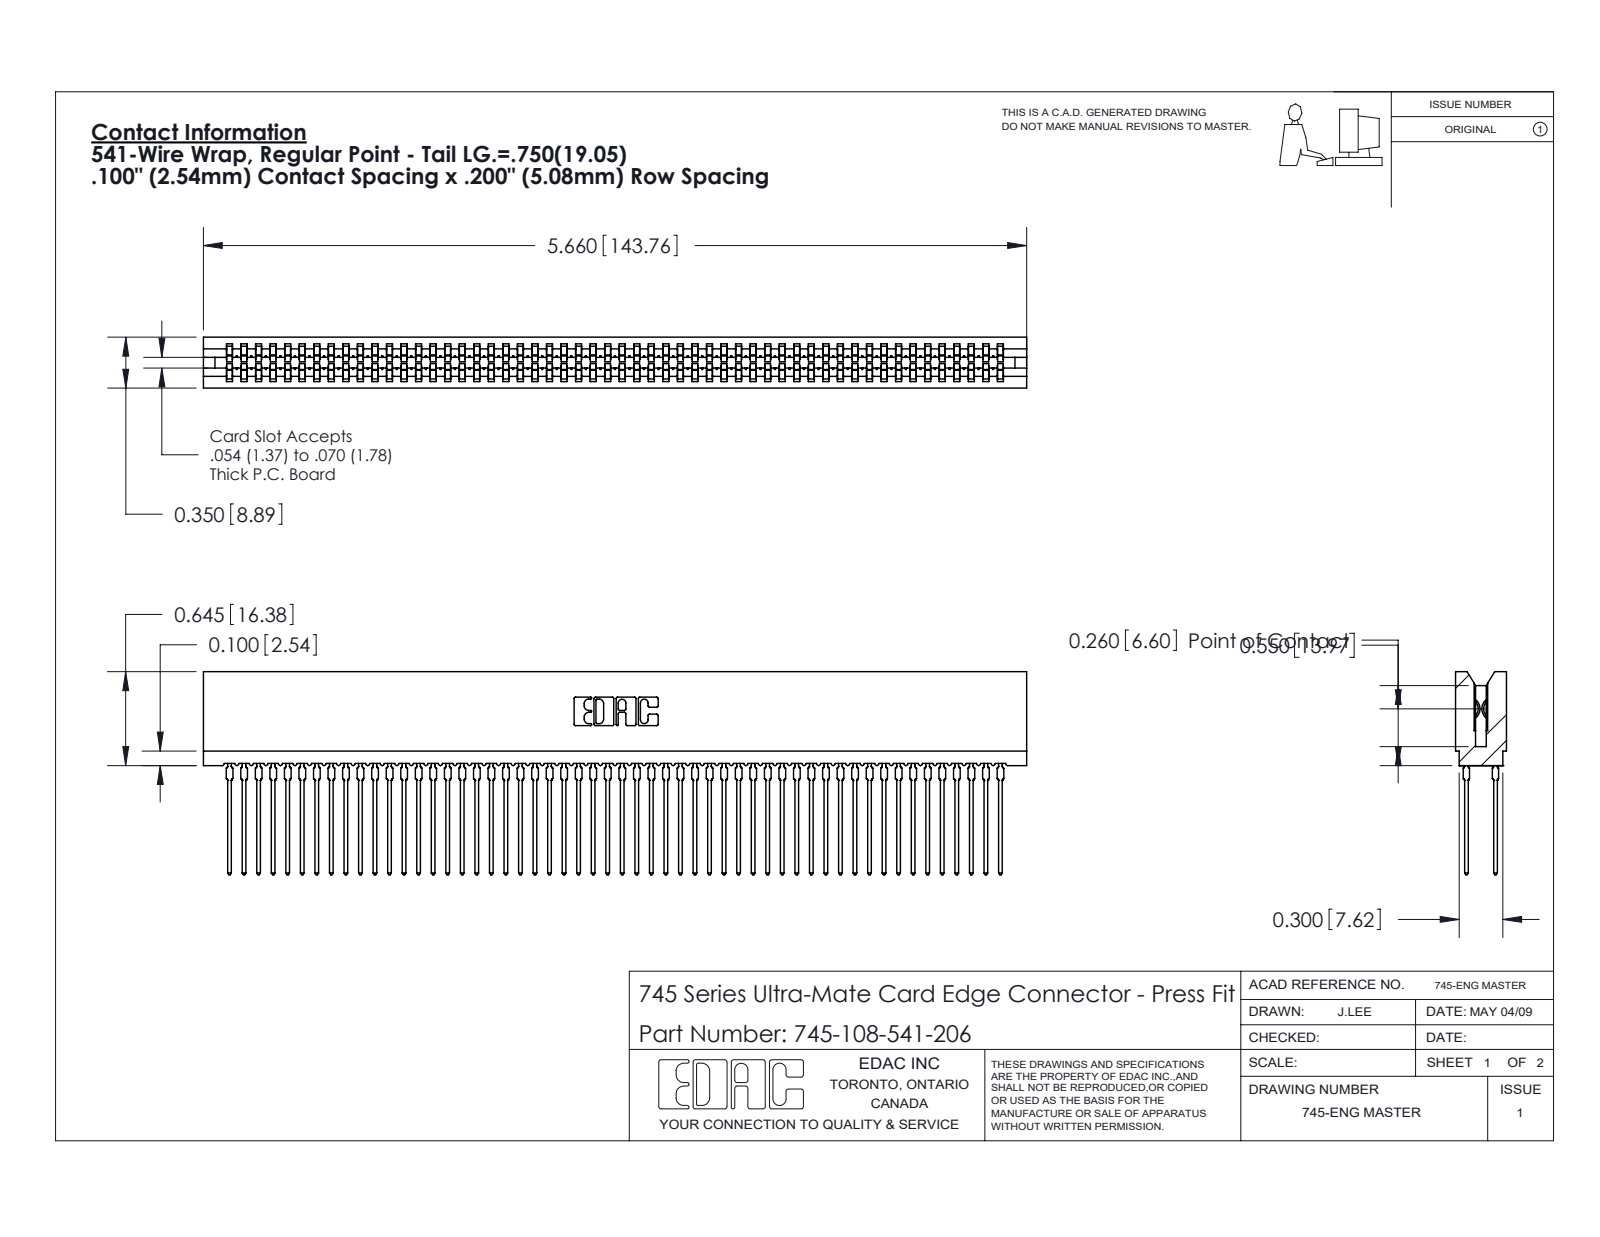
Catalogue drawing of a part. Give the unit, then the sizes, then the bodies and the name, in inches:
Units: inches
Overall size (bounding box): 5.66 × 1.396 × 0.35
Partial cylindrical surfaces — rounded edges, fillets, slot ends (radius × count): R0.021 ×216, R0.015 ×108, R0.01 ×22, R0.005 ×8, R0.011 ×8, R0.007 ×6, R0.031 ×6, R0.026 ×3
Main face-to-face distances: 0.063, 0.287, 0.2, 0.35, 0.087, 0.263, 0.025, 0.045, 0.305, 0.018
Volume: 0.817 in³ · Surface area: 45.96 in²
Bodies: 109 solids, 9762 faces (5024 planar, 1930 cylindrical, 2808 other)
Part name (STEP PRODUCT): 745-292-001_541; 745 Part_Insulator Option - 06; 745-108-541-206
STEP written by: SolidWorks 2020 (CONFIG_CONTROL_DESIGN)
